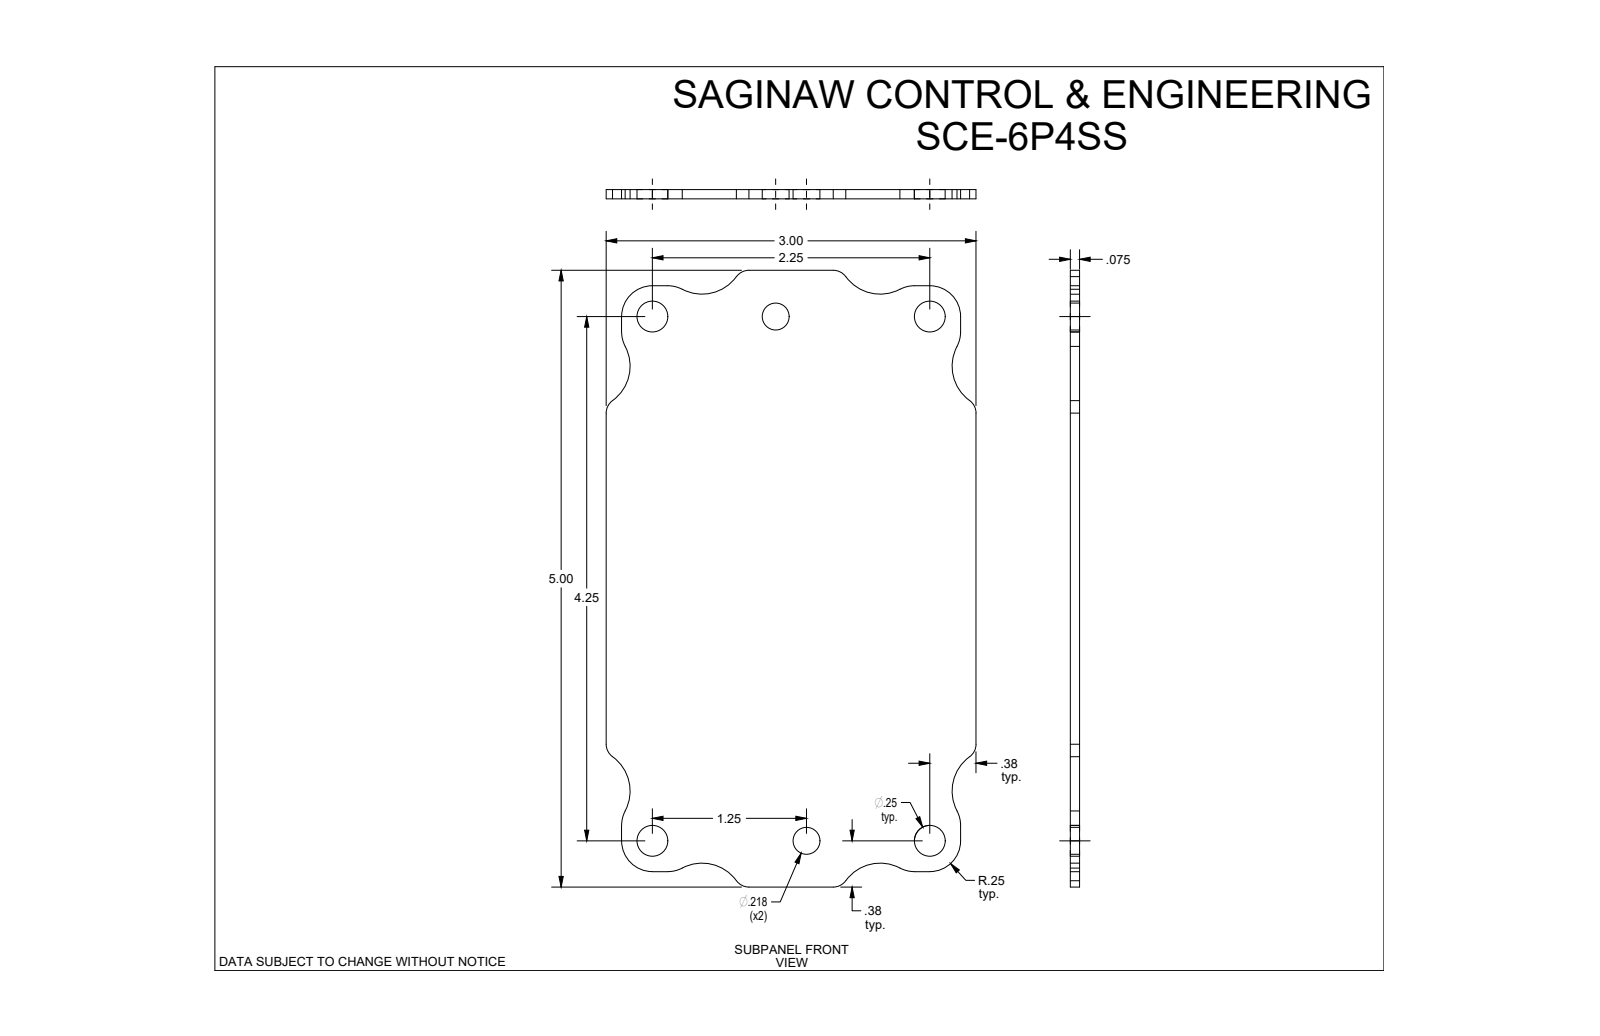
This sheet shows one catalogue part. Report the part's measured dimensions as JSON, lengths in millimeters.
{"part_name": "SCE-6P4SS", "step_written_by": "SolidWorks 2019 (CONFIG_CONTROL_DESIGN)", "units": "millimeters", "bodies": {"solids": 1, "faces": 48, "planar": 14, "cylindrical": 34, "other": 0}, "overall_size": [127, 76.2, 1.9], "volume_mm3": 16630, "surface_area_mm2": 18410, "round_holes": [[6.4, 4], [5.5, 2]], "partial_cylinders_radius": [[6.4, 12], [3.2, 8], [8.7, 8]], "face_to_face_distances": [1.9, 76.2, 3.2, 127, 123.8, 73, 120.7, 69.9], "hole_center_spacings": [25.4, 31.8, 57.2, 108, 110.9, 112.5, 122.1, 108.1]}
